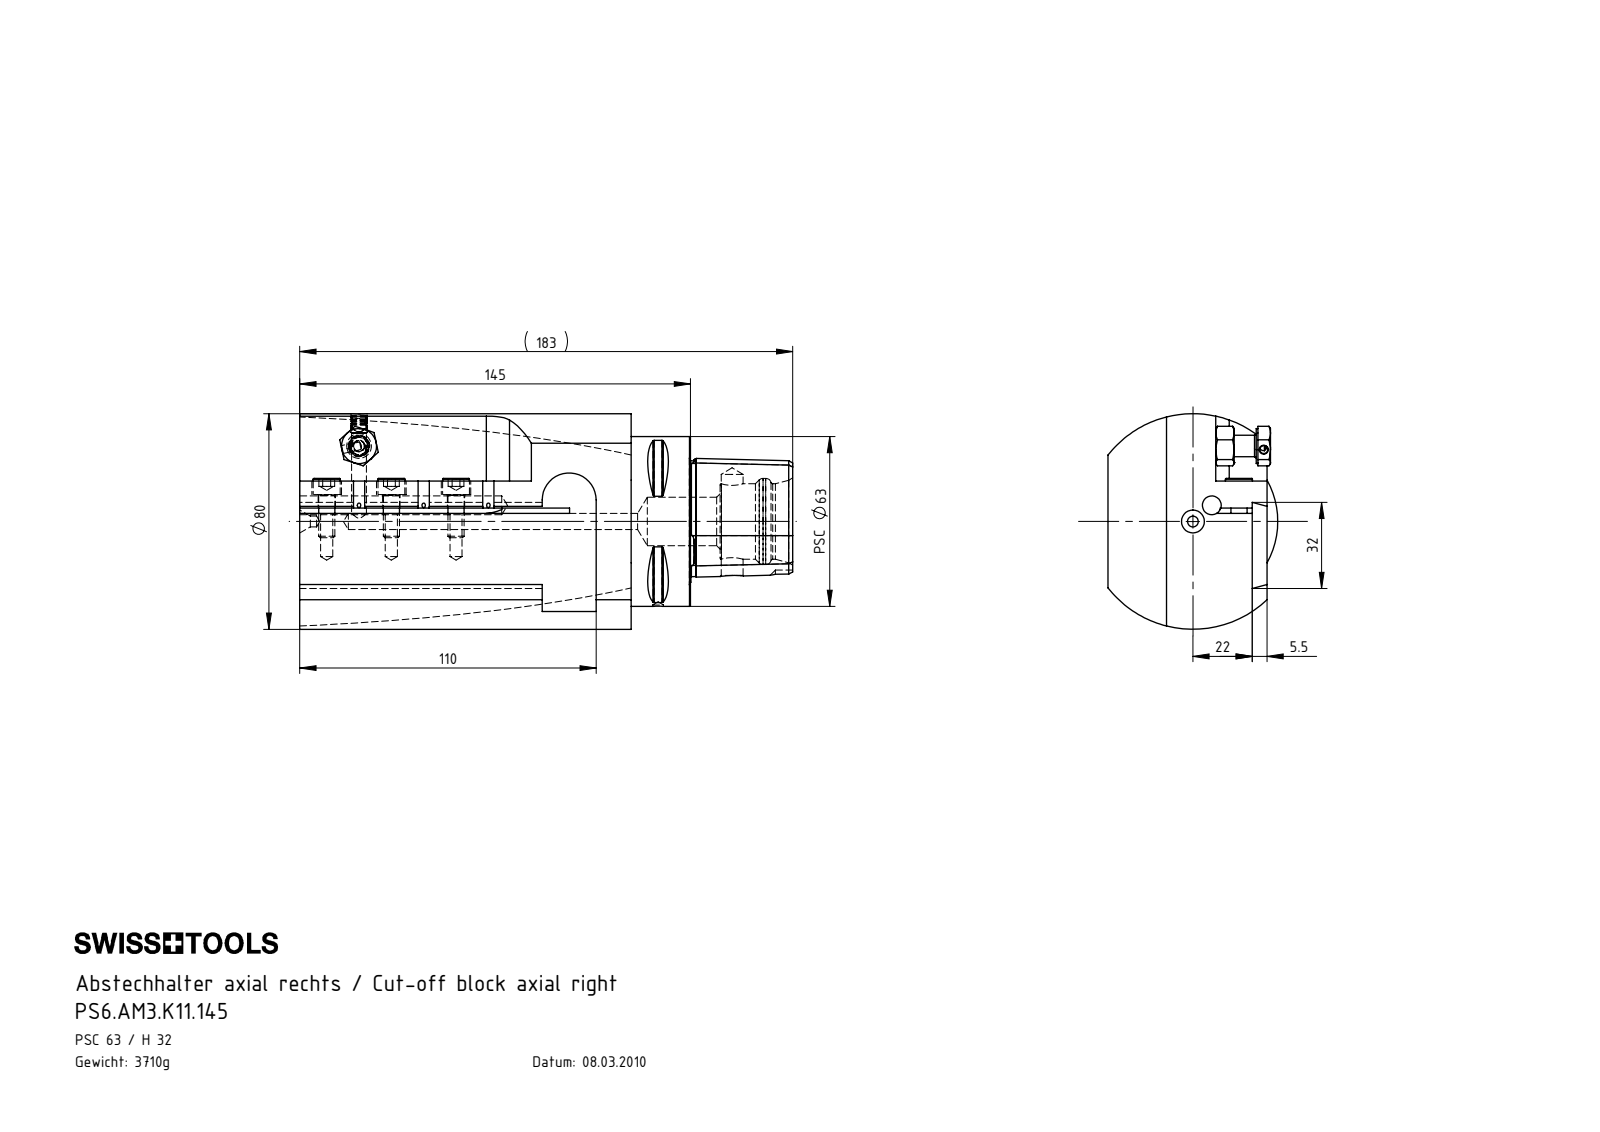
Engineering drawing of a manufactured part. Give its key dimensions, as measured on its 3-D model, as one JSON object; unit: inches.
{"part_name": "KVT_MB_600_060; ISO 4762 - M6 x 16_PreviewCfg; ISO 4035 - M8_PreviewCfg; AM3-ER1.001.020_PreviewCfg (+2 more)", "step_written_by": "SolidWorks 2017 (AUTOMOTIVE_DESIGN)", "units": "inches", "bodies": {"solids": 8, "faces": 390, "planar": 122, "cylindrical": 94, "other": 174}, "overall_size": [7.205, 3.15, 2.527], "volume_in3": 29.25, "surface_area_in2": 98.65, "round_holes": [[0.252, 4], [0.177, 3], [0.433, 3], [0.157, 2], [0.276, 2], [0.079, 1], [0.118, 1], [0.197, 1], [0.236, 1], [0.319, 1], [0.709, 1], [1.102, 1]], "round_bosses_or_shafts": [[0.236, 4], [0.394, 3], [2.48, 1], [0.512, 1], [0.315, 1]], "partial_cylinders_radius": [[0.02, 8], [0.083, 3], [0.236, 1], [0.394, 1], [1.575, 1], [3.051, 1]], "face_to_face_distances": [0.531, 0.748, 0.217, 5.709, 0.472, 0.866, 4.843, 0.079, 0.394, 0.945], "hole_center_spacings": [0.819, 0.945, 0.363, 1.083, 1.567, 1.89, 3.028, 3.955]}
